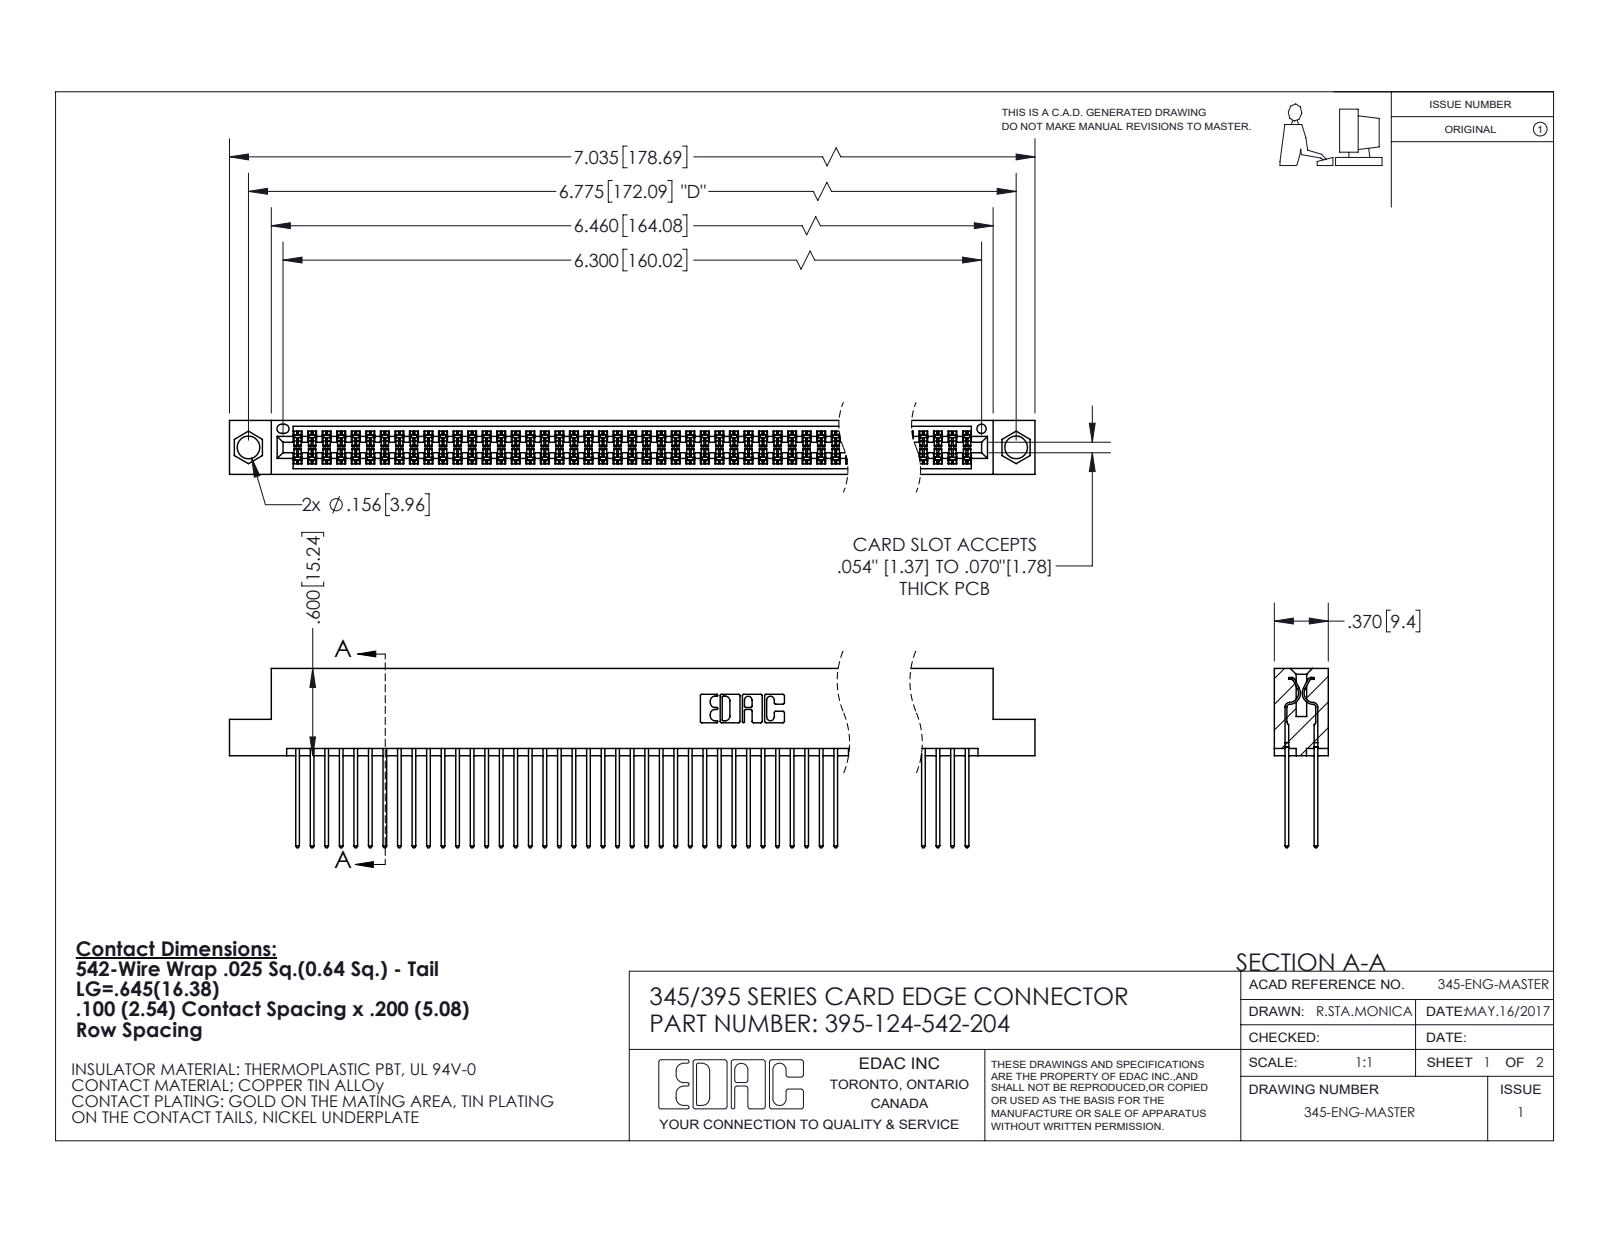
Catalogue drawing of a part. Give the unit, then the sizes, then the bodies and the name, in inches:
Units: inches
Overall size (bounding box): 7.035 × 1.232 × 0.37
Round holes (diameter × count): ⌀0.156 ×2, ⌀0.064 ×1
Partial cylindrical surfaces — rounded edges, fillets, slot ends (radius × count): R0.006 ×186, R0.01 ×124, R0.01 ×22, R0.007 ×6, R0.031 ×6, R0.026 ×3, R0.014 ×2, R0.019 ×2
Main face-to-face distances: 0.072, 0.298, 0.2, 0.098, 0.272, 0.025, 0.225, 0.37, 0.175, 0.149
Hole centre spacings: 0.27, 6.539, 6.775
Volume: 1.099 in³ · Surface area: 45.83 in²
Bodies: 125 solids, 6340 faces (4186 planar, 2154 cylindrical, 0 other)
Part name (STEP PRODUCT): 345-292-001_345-293-142; 345 Part_Flush Mounting Lugs - 0.156 Dia-TI; 395-124-542-204
STEP written by: SolidWorks 2020 (CONFIG_CONTROL_DESIGN)
